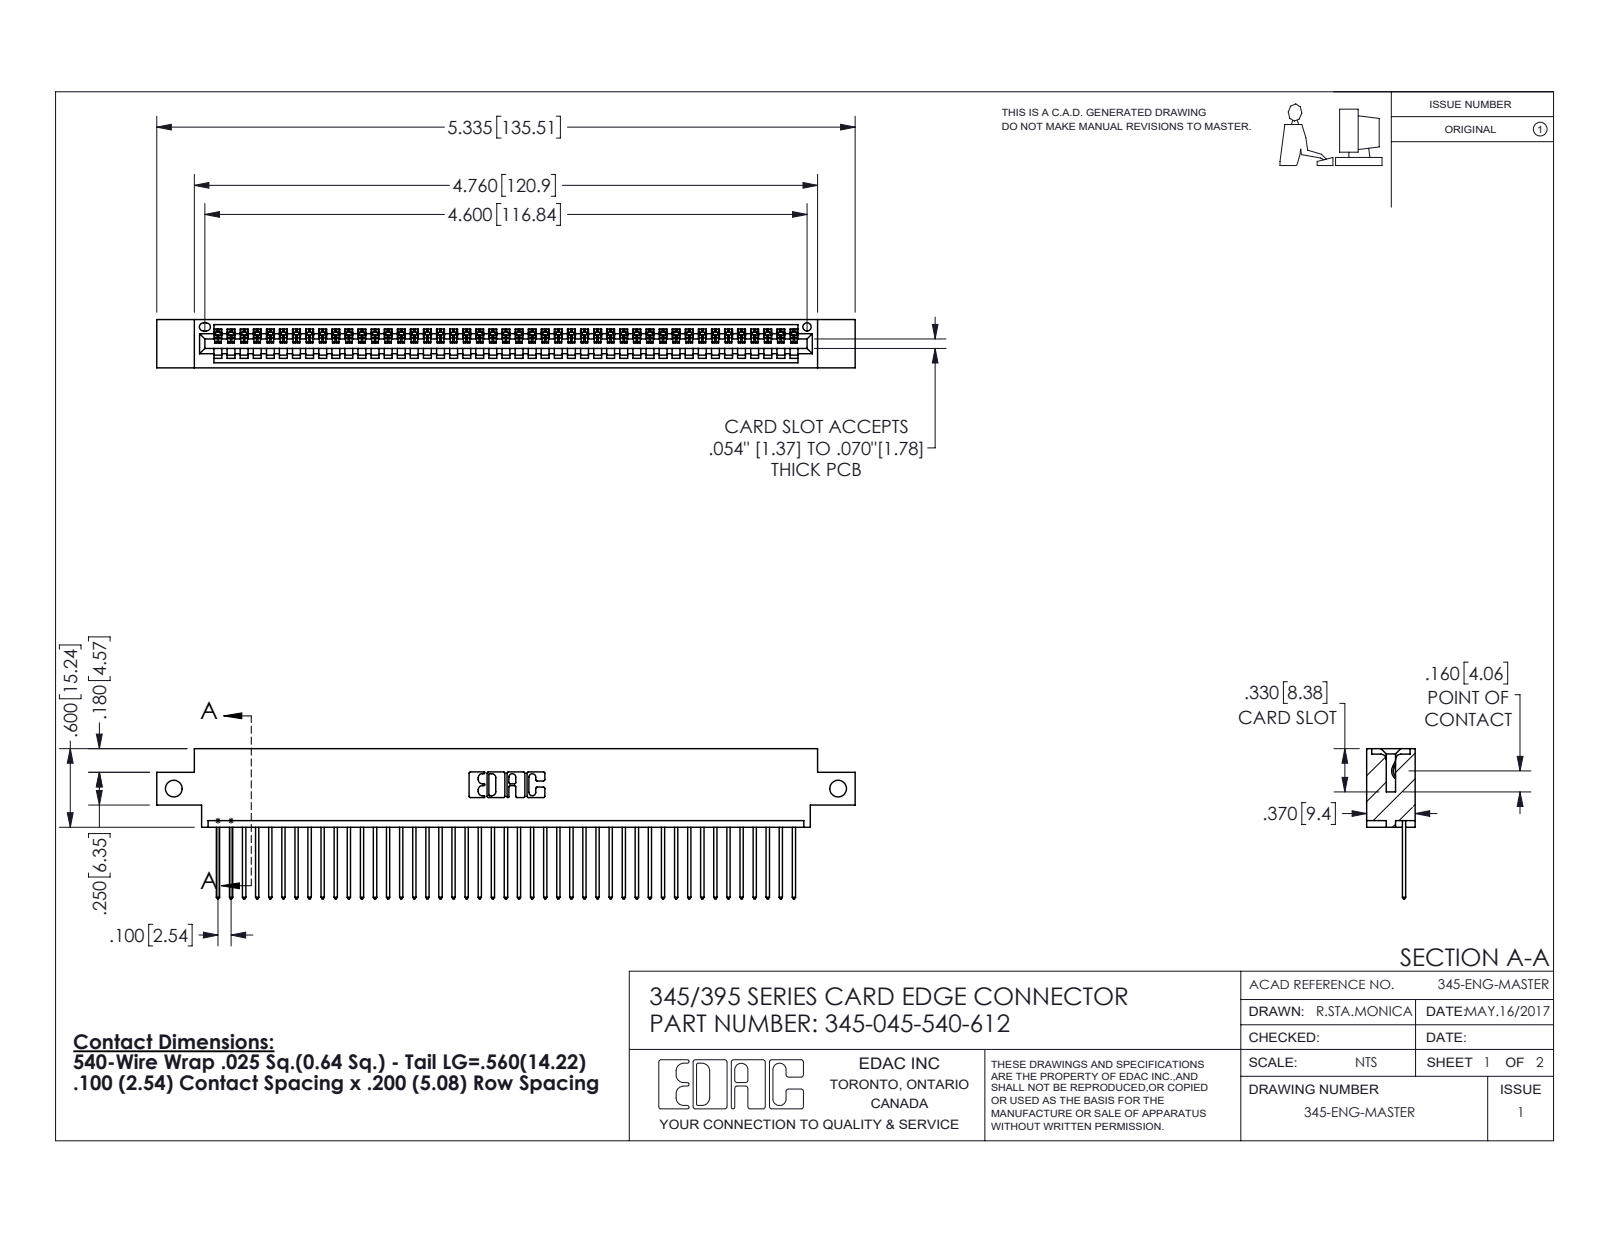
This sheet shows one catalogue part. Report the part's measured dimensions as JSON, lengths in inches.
{"part_name": "345-045-540-612; 345 Part_0.170 Offset - Side Mount; 345-292-001_345-293-140", "step_written_by": "SolidWorks 2016 (CONFIG_CONTROL_DESIGN)", "units": "inches", "bodies": {"solids": 46, "faces": 2740, "planar": 1884, "cylindrical": 856, "other": 0}, "overall_size": [5.335, 1.147, 0.37], "volume_in3": 0.778, "surface_area_in2": 26.99, "round_holes": [[0.128, 2], [0.064, 1]], "partial_cylinders_radius": [[0.006, 90], [0.01, 90], [0.01, 22], [0.007, 6], [0.031, 6], [0.026, 3], [0.031, 2], [0.04, 2]], "face_to_face_distances": [0.072, 0.298, 0.37, 0.098, 0.272, 0.025, 0.2, 0.225, 0.175, 0.149], "hole_center_spacings": [5.075]}
